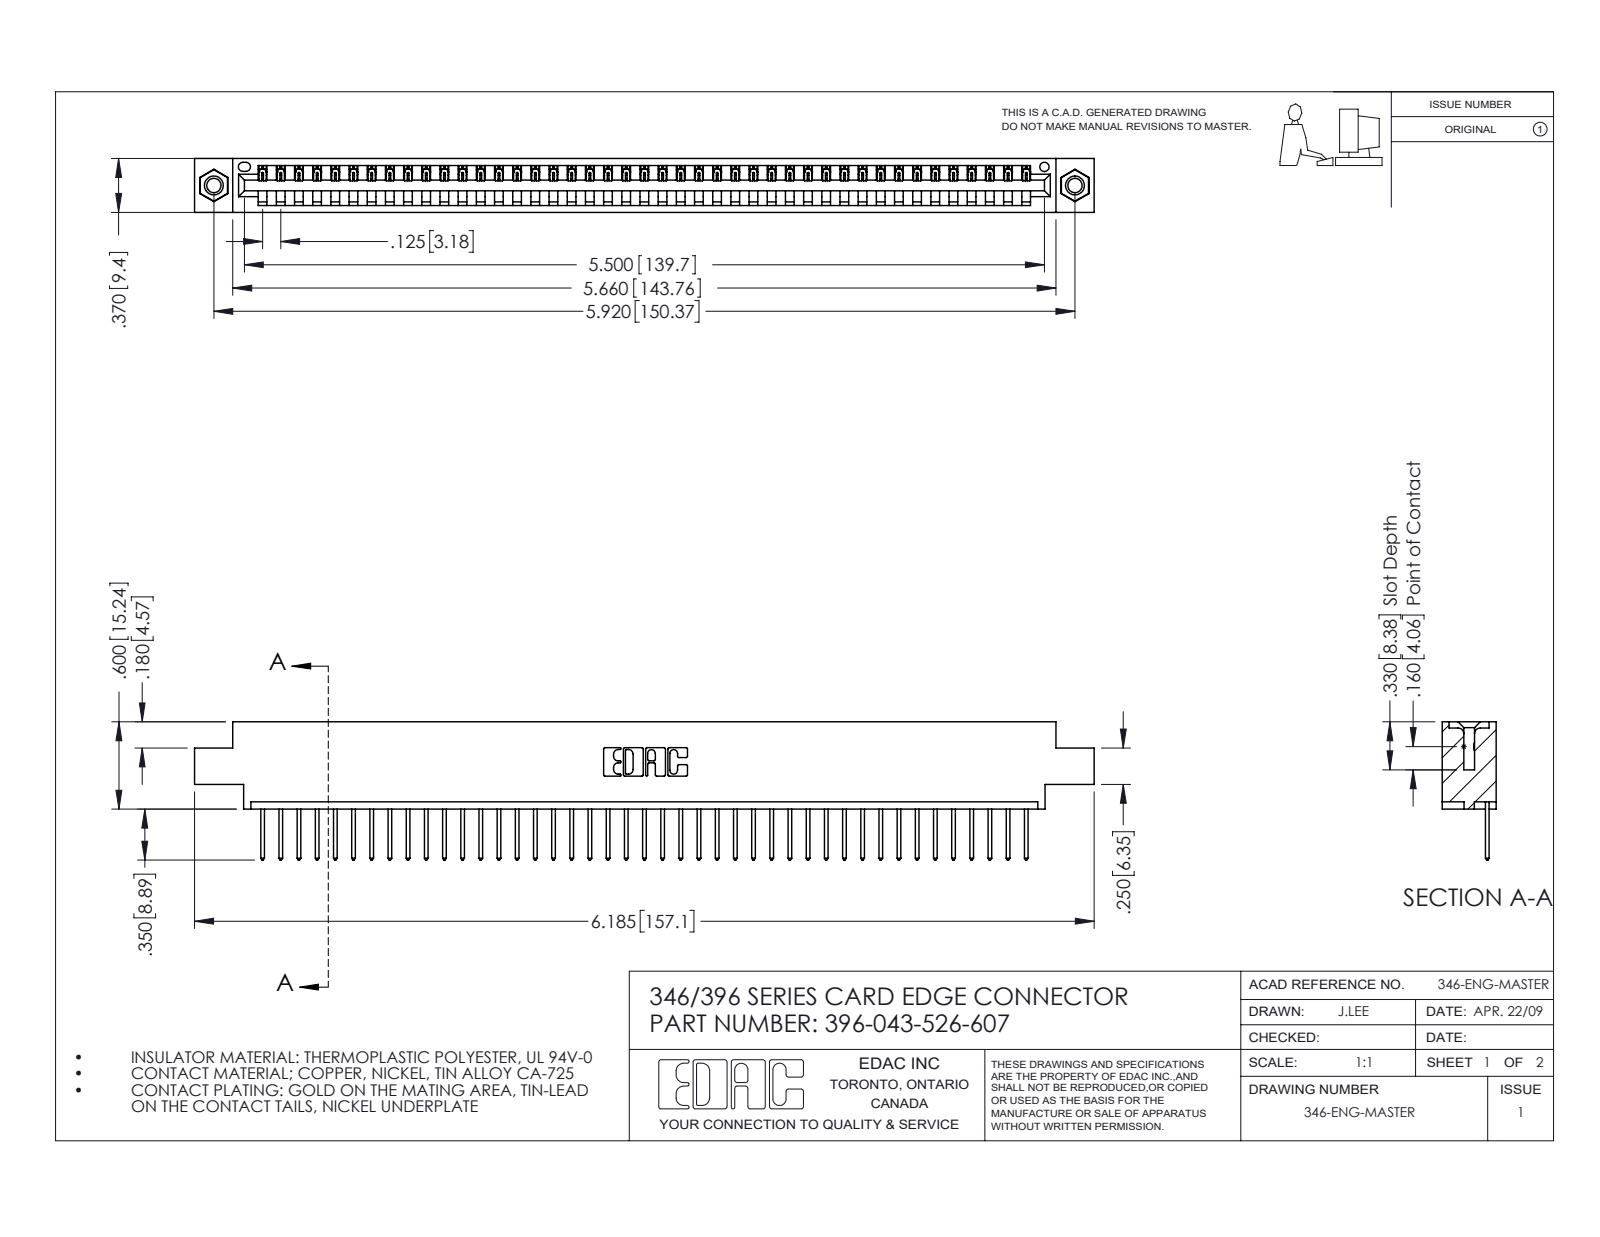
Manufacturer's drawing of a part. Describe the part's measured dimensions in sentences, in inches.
The part is named "346 Part_0.170 Offset - 0.156 Dia-TI; 396-043-526-607; 345-292-001_345-293-126; 345-250-001_345-250-005-103". Its 3-D file was written by "SolidWorks 2016 (CONFIG_CONTROL_DESIGN)". It is 46 solids with 2680 faces: 1832 planar, 832 cylindrical and 16 other. Overall it measures 6.185 by 0.95 by 0.37 inches. Its volume is 0.906 cubic inches and its surface area 29.01 square inches. Round holes: 2 of diameter 0.098, 2 of diameter 0.125, 2 of diameter 0.156, 1 of diameter 0.064. Round bosses or shafts: 2 of diameter 0.155. Partial cylindrical surfaces (rounded edges, fillets, slot ends): 86 of radius 0.006, 86 of radius 0.01, 22 of radius 0.01, 6 of radius 0.007, 6 of radius 0.031, 3 of radius 0.026, 2 of radius 0.031, 2 of radius 0.04. The main face-to-face distances are 0.048, 0.322, 0.37, 0.25, 0.072, 0.298, 0.025, 0.222, 0.148, 0.1. The hole center spacings are 0.246, 5.711, 5.92.
